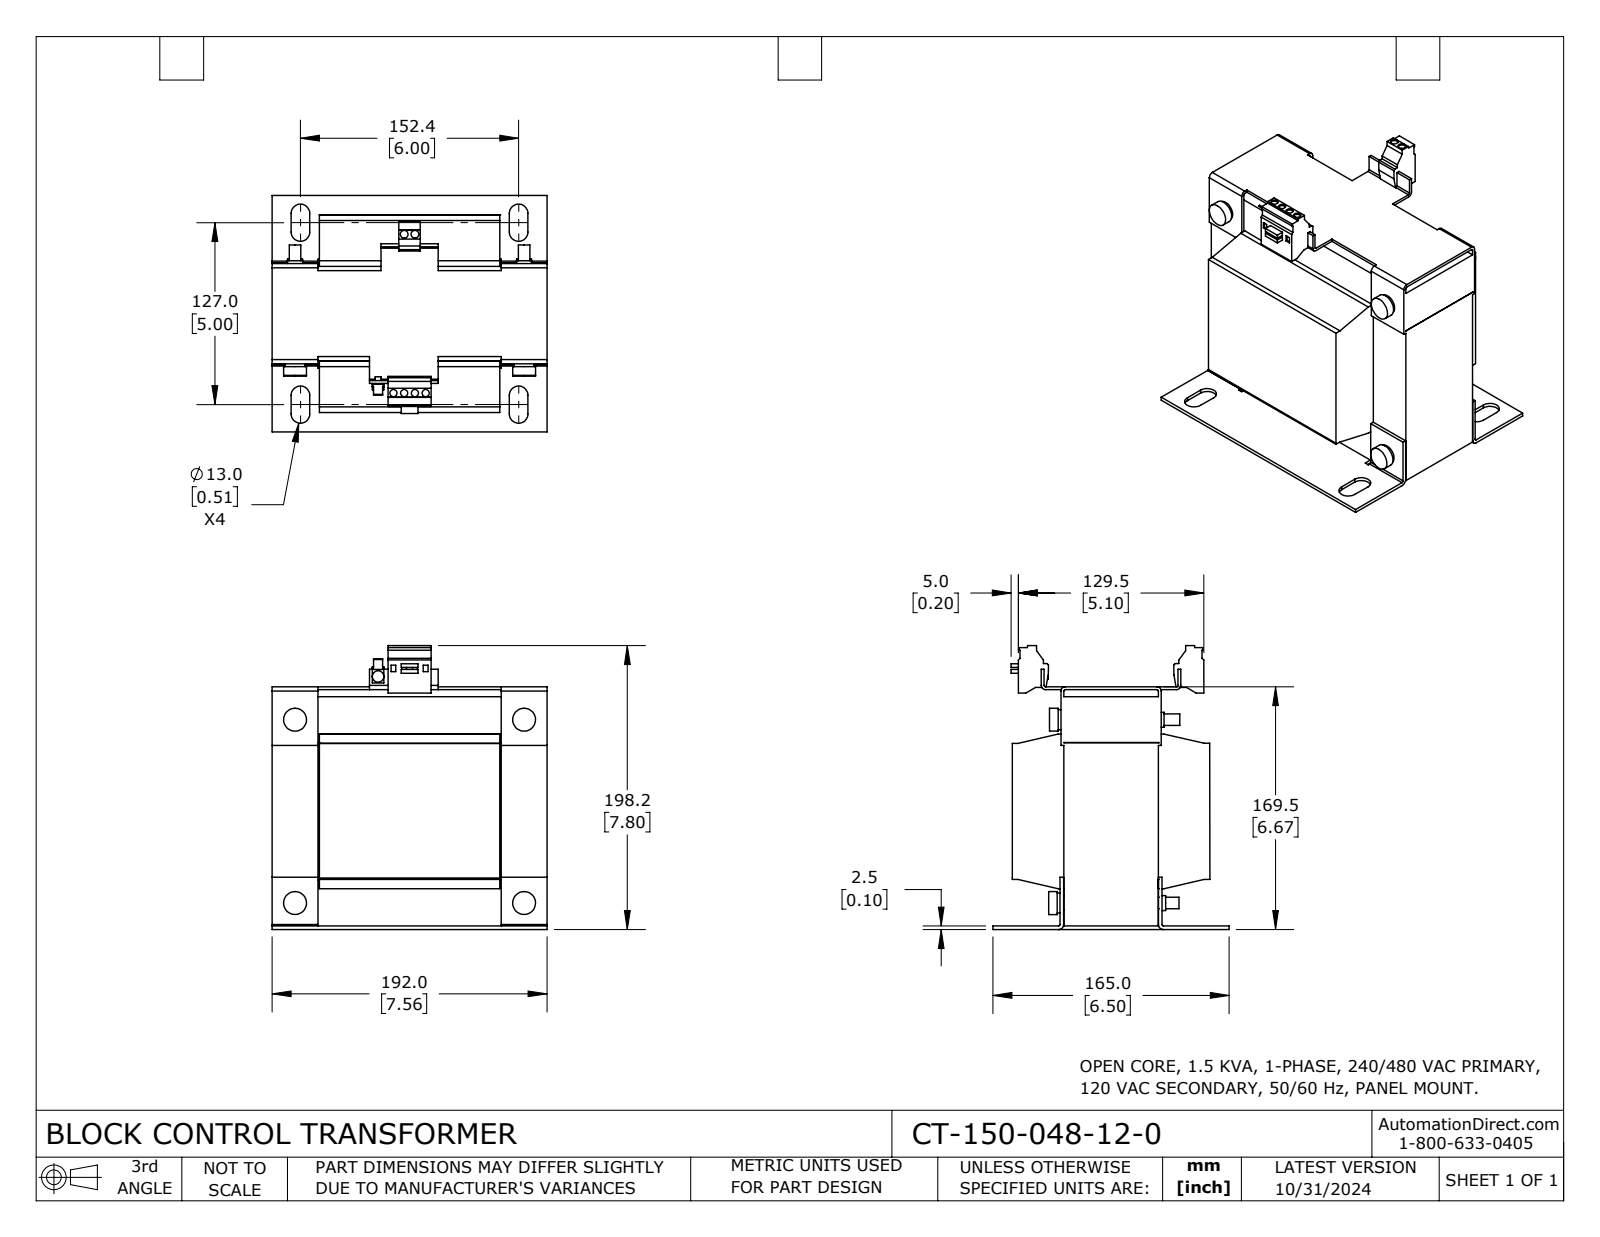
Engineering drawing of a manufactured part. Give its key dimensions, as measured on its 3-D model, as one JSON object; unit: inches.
{"part_name": "CT-150-048-12-0", "step_written_by": "SolidWorks 2023 (CONFIG_CONTROL_DESIGN)", "units": "inches", "bodies": {"solids": 1, "faces": 330, "planar": 238, "cylindrical": 92, "other": 0}, "overall_size": [7.803, 7.559, 6.496], "volume_in3": 187.8, "surface_area_in2": 446.9, "round_holes": [[0.197, 4], [0.213, 2]], "round_bosses_or_shafts": [[0.315, 5], [0.63, 4], [0.551, 4], [0.413, 4], [0.394, 2], [0.157, 1]], "partial_cylinders_radius": [[0.256, 8], [0.039, 6], [0.118, 4], [0.138, 2]], "face_to_face_distances": [5.039, 1.26, 6.299, 0.098, 1.416, 4.015, 1.299, 6.26, 5.138, 0.079], "hole_center_spacings": [0.295, 4.376, 0.591, 4.366, 4.406, 0.886]}
